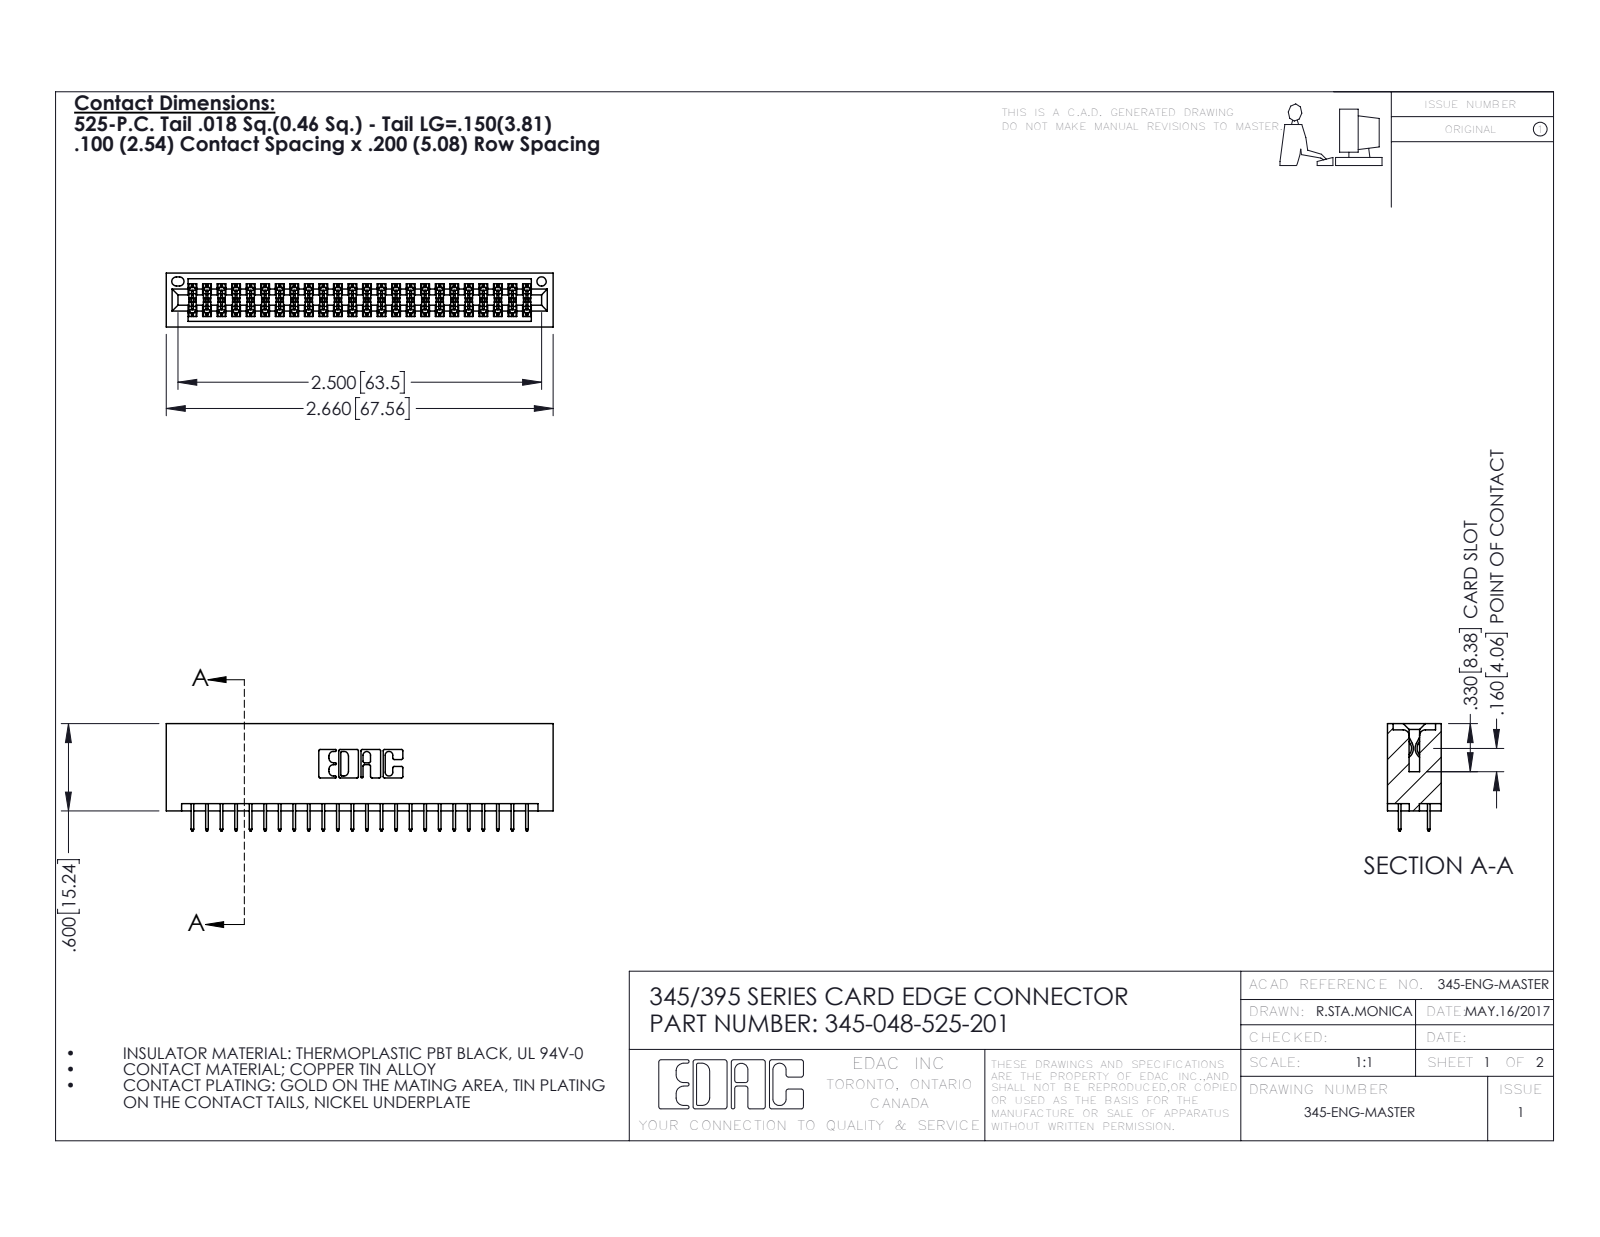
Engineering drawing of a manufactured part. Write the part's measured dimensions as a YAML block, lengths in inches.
part_name: "345 Part_No Mounting Lugs; 345-048-525-201; 345-292-001_345-293-125"
step_written_by: "SolidWorks 2020 (CONFIG_CONTROL_DESIGN)"
units: inches
bodies: {solids: 49, faces: 2710, planar: 1948, cylindrical: 762, other: 0}
overall_size: [2.66, 0.737, 0.37]
volume: 0.423
surface_area: 15.45
round_holes:
  - {diameter: 0.064, count: 1}
partial_cylinders:
  - {radius: 0.006, count: 72}
  - {radius: 0.01, count: 22}
  - {radius: 0.007, count: 6}
  - {radius: 0.031, count: 6}
  - {radius: 0.026, count: 3}
  - {radius: 0.014, count: 2}
  - {radius: 0.019, count: 2}
  - {radius: 0.022, count: 2}
face_to_face_distances: [0.298, 0.072, 0.2, 0.37, 0.098, 0.272, 0.025, 0.225, 0.072, 0.175]
